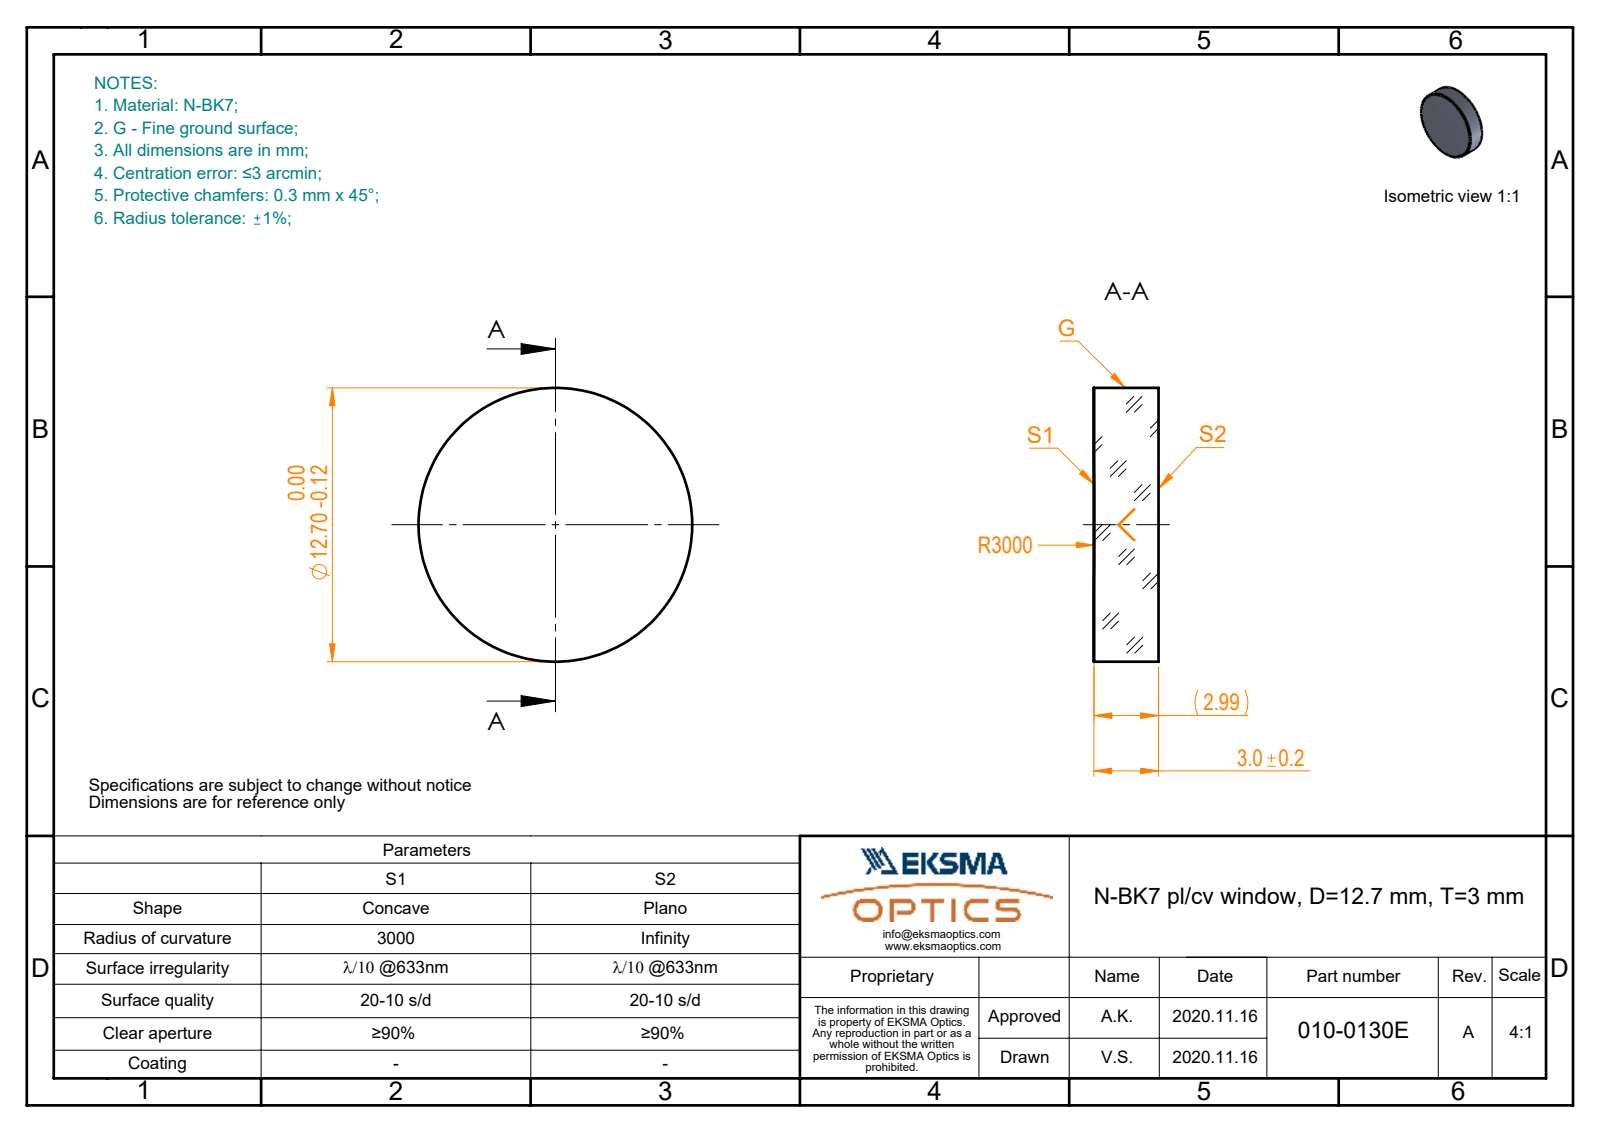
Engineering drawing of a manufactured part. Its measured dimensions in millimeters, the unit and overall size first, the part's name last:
Units: millimetres
Overall size (bounding box): 12.7 × 12.7 × 3
Round bosses / shafts (diameter × count): ⌀12.7 ×1
Volume: 380 mm³ · Surface area: 373 mm²
Bodies: 1 solid, 5 faces (1 planar, 2 cylindrical, 2 other)
Part name (STEP PRODUCT): 010-0130E_N-BK7_PCV_window
STEP written by: SolidWorks 2019 (CONFIG_CONTROL_DESIGN)
